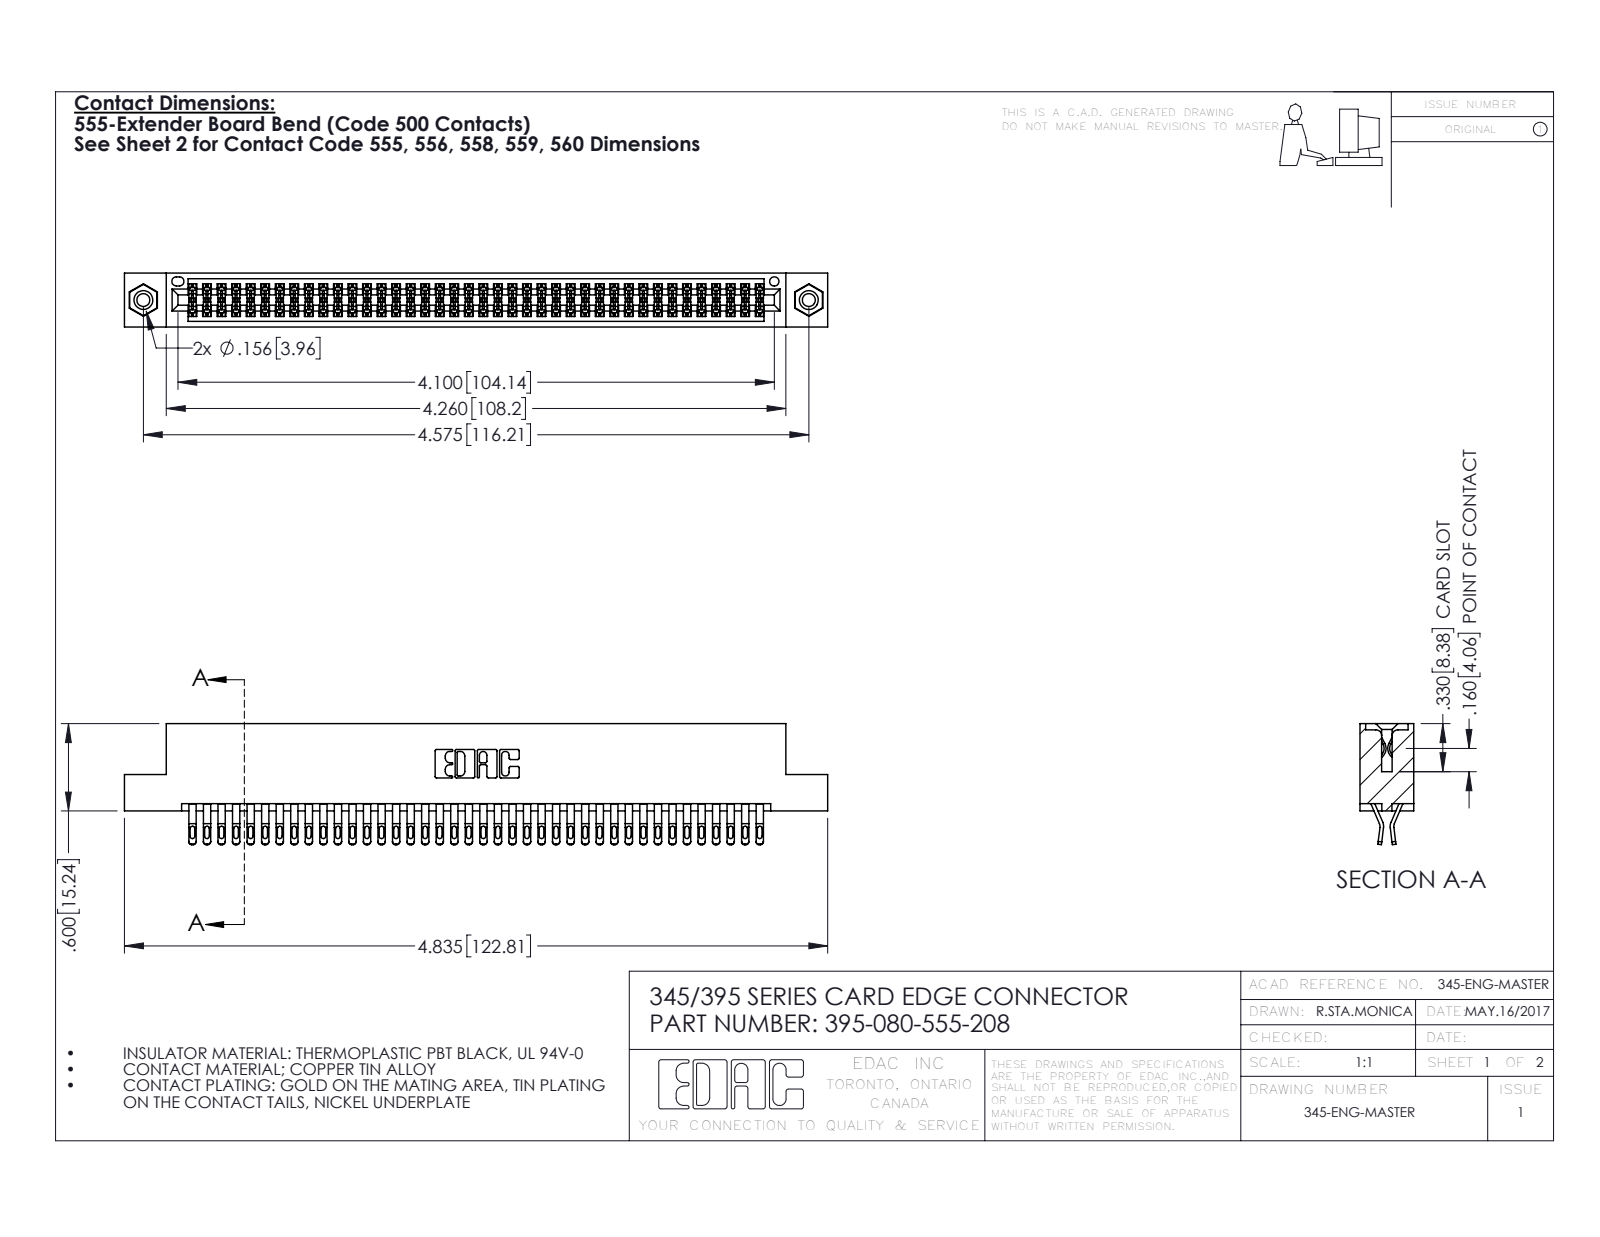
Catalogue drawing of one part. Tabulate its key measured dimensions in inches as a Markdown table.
| quantity | value |
| --- | --- |
| part name | 395-080-555-208; 345-250-001_345-250-003-102; 345-292-001_555 Tail; 345 Part_Flush Mounting Lugs - 0.156 Dia-TI |
| STEP written by | SolidWorks 2016 (CONFIG_CONTROL_DESIGN) |
| units | inches |
| bodies | 83 solids, 4666 faces (2592 planar, 2058 cylindrical, 16 other) |
| overall size | 4.835 × 0.832 × 0.37 |
| volume | 0.741 in³ |
| surface area | 29.02 in² |
| round holes (diameter × count) | 0.089 × 2, 0.125 × 2, 0.156 × 2, 0.064 × 1 |
| round bosses / shafts (diameter × count) | 0.155 × 2 |
| partial cylindrical surfaces (radius × count) | 0.016 × 200, 0.02 × 160, 0.006 × 120, 0.01 × 22, 0.007 × 6, 0.031 × 6, 0.026 × 3, 0.01 × 2 |
| main face-to-face distances | 0.072, 0.298, 0.2, 0.025, 0.37, 0.098, 0.272, 0.225, 0.175, 0.149 |
| hole center spacings | 0.27, 4.339, 4.575 |
